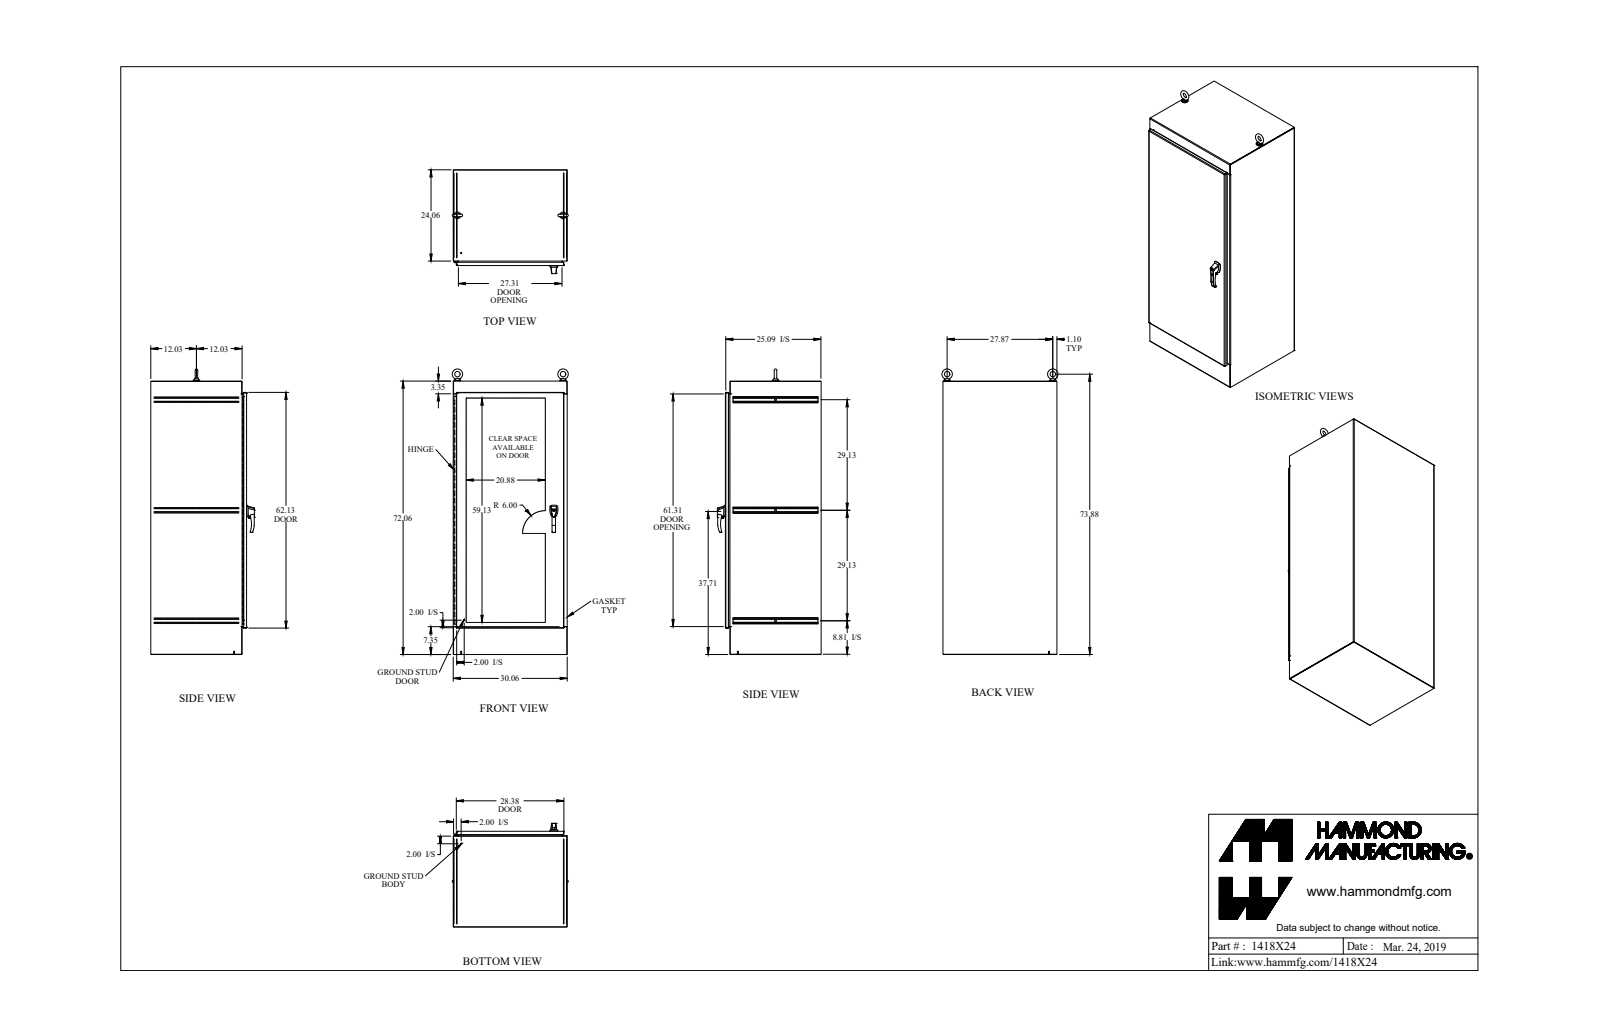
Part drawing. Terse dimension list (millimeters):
name: 1418X24_Default
written by: SolidWorks 2019 (CONFIG_CONTROL_DESIGN)
unit: mm
bodies: 52 solids, 1742 faces (781 planar, 796 cylindrical, 165 other)
size: 1923.1 × 790.4 × 695
volume: 17 110 000 mm³; area: 14 160 000 mm²
holes: 10× ⌀7.7, 4× ⌀19.1, 3× ⌀12.7, 2× ⌀6.4, 2× ⌀6.5, 2× ⌀7.1, 2× ⌀7.1, 2× ⌀8, 2× ⌀9.9, 2× ⌀10.5, 2× ⌀13.4, 2× ⌀15.9
bosses: 4× ⌀7.1, 2× ⌀44.5, 2× ⌀38.1, 2× ⌀31.8, 2× ⌀25.4, 2× ⌀19.1, 2× ⌀18.7, 2× ⌀16
rounds: 42× R1.1, 36× R3.5, 22× R3.2, 16× R0.5, 14× R1.2, 14× R3.6, 10× R1.5, 7× R8.1
face distances: 2.4, 761.1, 2.4, 758.7, 636.4, 638.9, 638.9, 641.3, 763.5, 1827.9
hole spacings: 152.4, 304.8, 457.2, 609.6, 762, 707.9, 914.4, 1066.8
